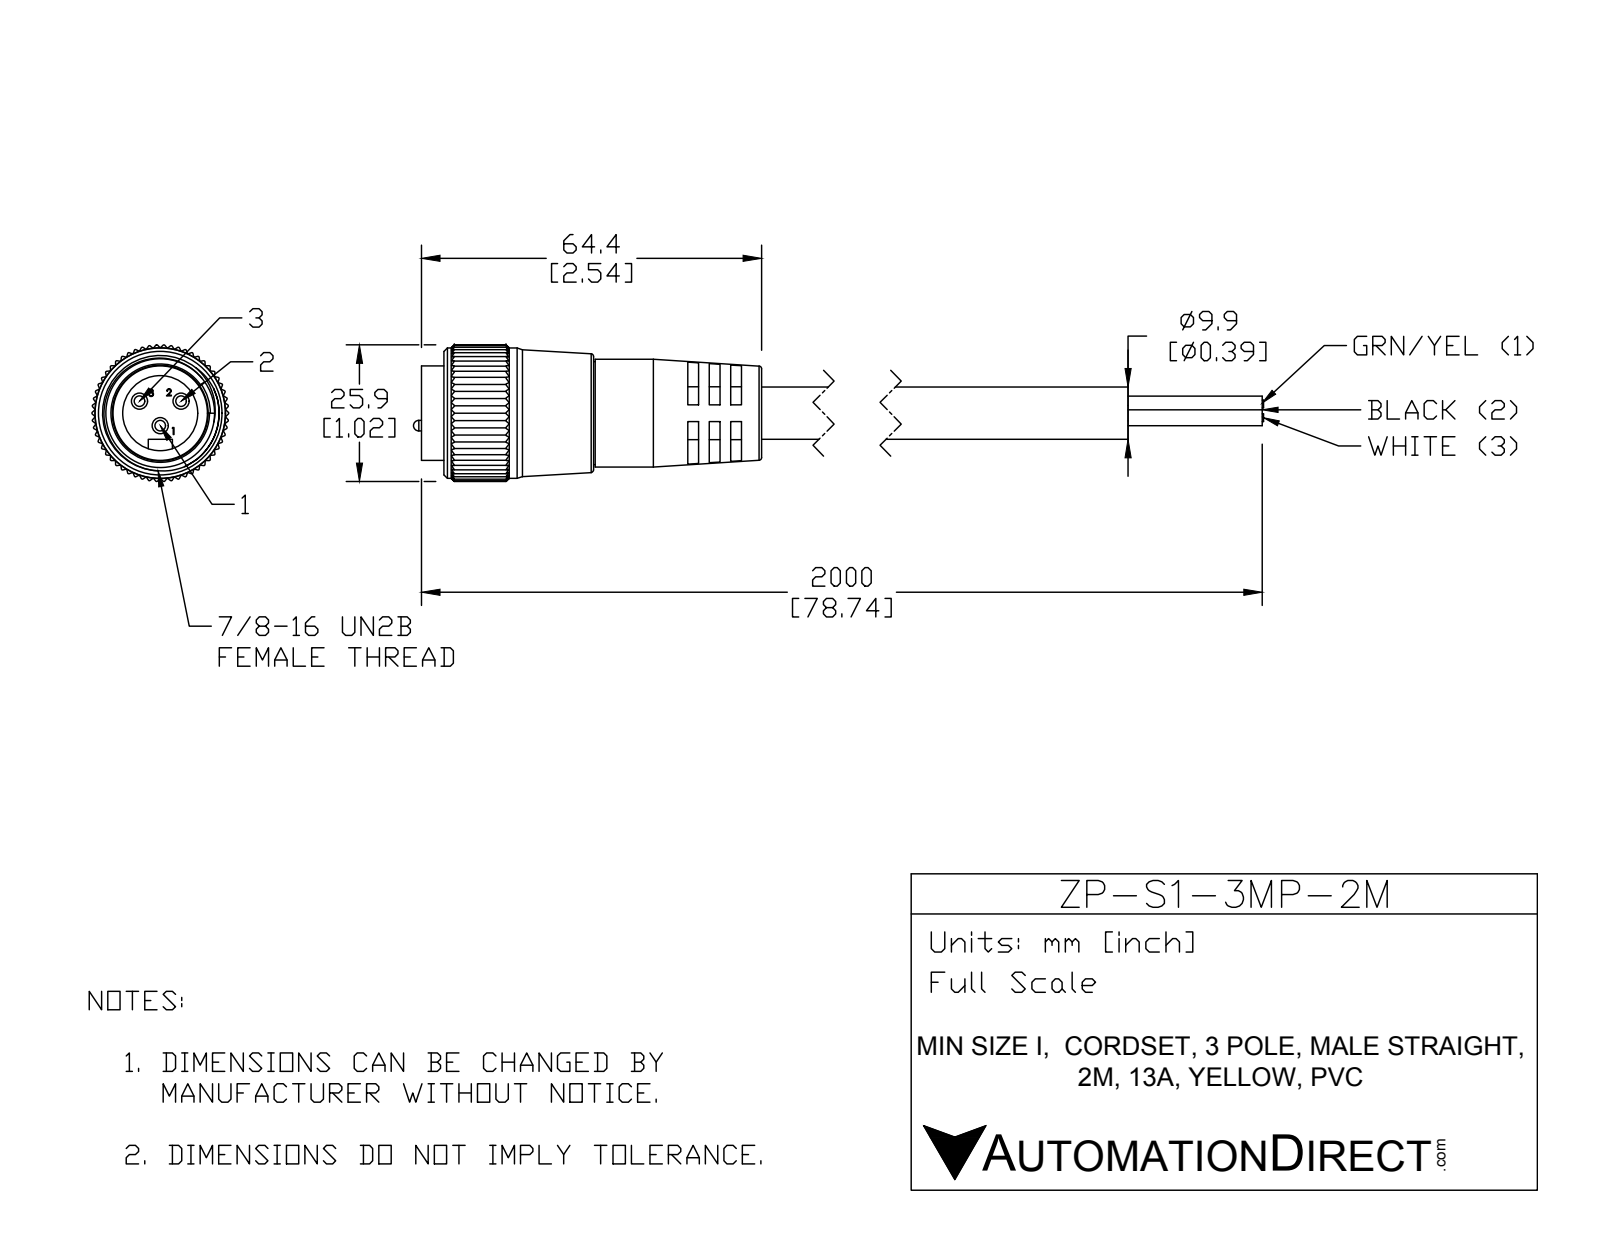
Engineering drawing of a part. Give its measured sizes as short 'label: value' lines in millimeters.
name: ZP-S1-3MP-2M
written by: SolidWorks 2015 (AUTOMOTIVE_DESIGN)
unit: mm
bodies: 5 solids, 564 faces (196 planar, 314 cylindrical, 54 other)
size: 109.62 × 52.91 × 25.84
volume: 27 012 mm³; area: 12 612 mm²
holes: 1× ⌀14.22, 1× ⌀19.96, 1× ⌀20.45, 1× ⌀21
bosses: 3× ⌀3.05, 3× ⌀2, 2× ⌀9.91, 1× ⌀24.68, 1× ⌀20.4, 1× ⌀19.5, 1× ⌀17.88
rounds: 165× R0.25, 1× R2.29, 1× R5.25, 1× R12.93
face distances: 2, 4.04, 13.88, 11.88, 2.04, 9.84, 6.04, 7.84, 6.06, 8.06
